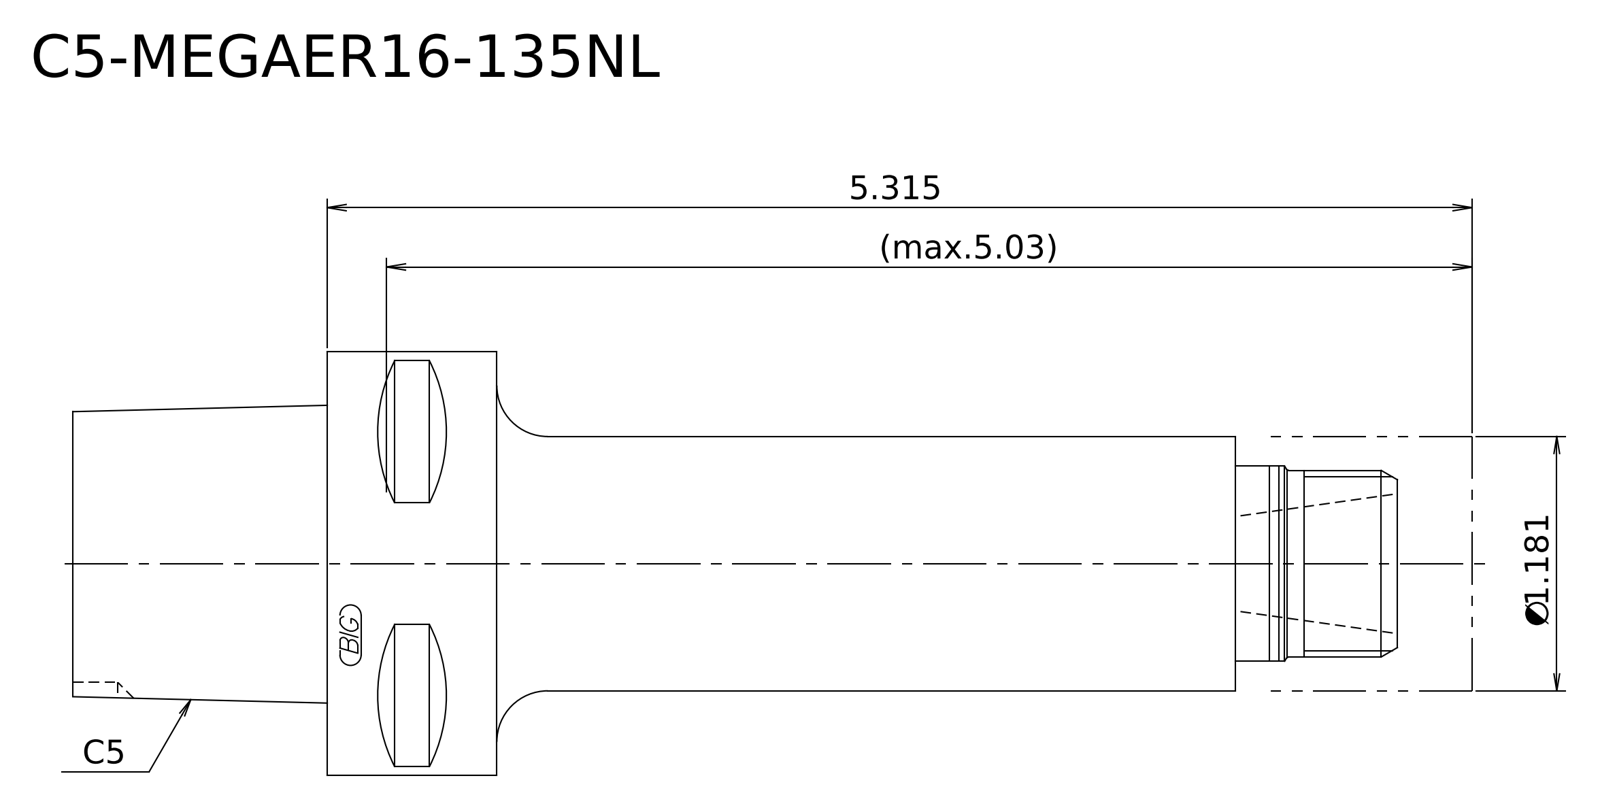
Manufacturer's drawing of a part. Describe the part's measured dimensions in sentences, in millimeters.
Its 3-D file was written by "Kubotek KeyCreator 2011 V10.0.2 (22737) (automotive_design)". It is 2 solids with 16 faces: 7 planar, 5 cylindrical and 4 other. Overall it measures 165 by 50 by 50 millimeters. Its volume is 155 042 cubic millimeters and its surface area 23 189 square millimeters. Round bosses or shafts: 1 of diameter 50, 1 of diameter 30, 1 of diameter 23, 1 of diameter 22. The main face-to-face distances are 30, 110, 140, 25, 135, 165, 115, 90, 20, 50.
